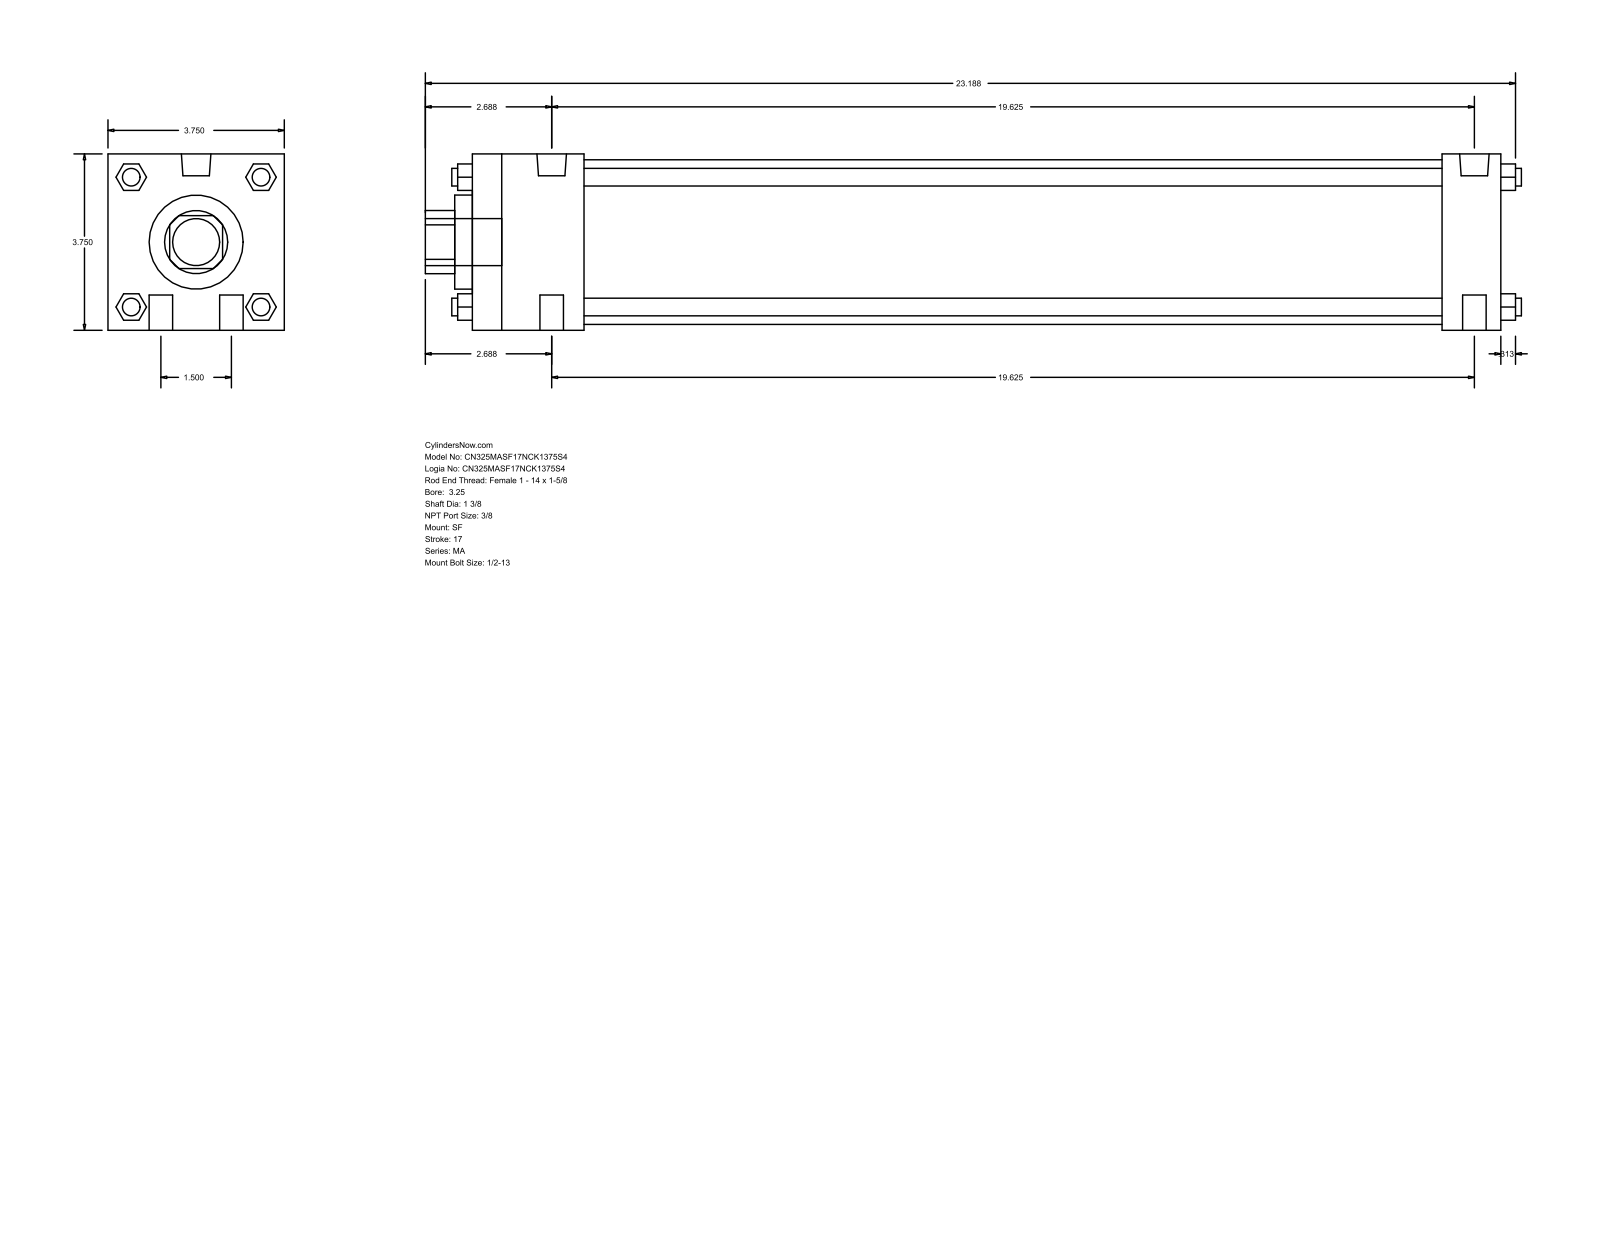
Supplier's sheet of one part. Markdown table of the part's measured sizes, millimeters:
| quantity | value |
| --- | --- |
| part name | MA_SF__0325_1.375 |
| STEP written by | GSSL Pune (CONFIG_CONTROL_DESIGN) |
| units | millimeters |
| bodies | 0 solids, 124 faces (94 planar, 30 cylindrical, 0 other) |
| overall size | 592.14 × 95.25 × 95.25 |
| round holes (diameter × count) | 34.92 × 1, 50.8 × 1, 88.9 × 1 |
| round bosses / shafts (diameter × count) | 12.7 × 4, 9.53 × 4, 15.93 × 2, 11.11 × 2, 25.4 × 1 |
| partial cylindrical surfaces (radius × count) | 17.06 × 1 |
| main face-to-face distances | 95.24, 555.62, 523.87, 31.75, 60.32, 463.55, 495.3, 9.52, 69.84, 533.39 |
